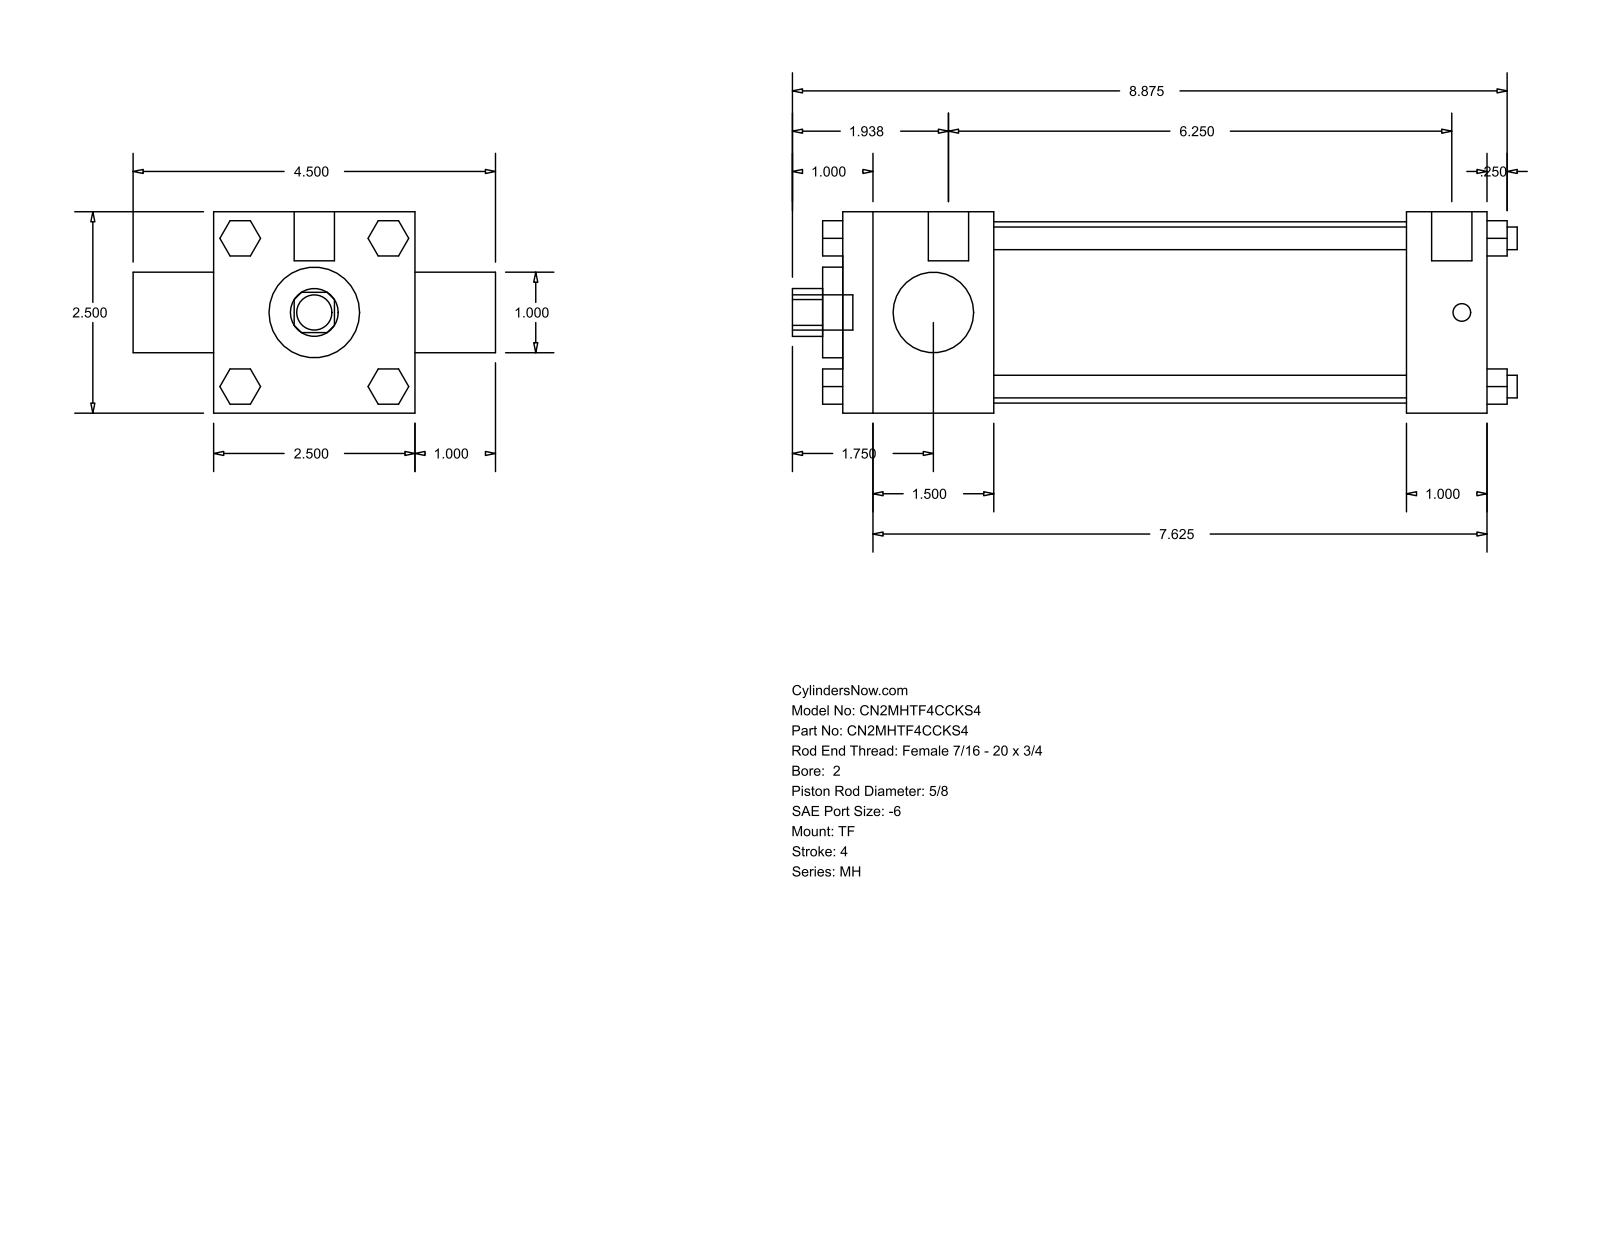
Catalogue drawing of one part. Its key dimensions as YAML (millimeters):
part_name: "MH_TF__0200_0.625"
step_written_by: "GSSL Pune (CONFIG_CONTROL_DESIGN)"
units: millimeters
bodies: {solids: 0, faces: 120, planar: 92, cylindrical: 28, other: 0}
overall_size: [228.6, 114.3, 63.5]
round_holes:
  - {diameter: 15.88, count: 1}
  - {diameter: 25.4, count: 1}
  - {diameter: 28.57, count: 1}
  - {diameter: 57.15, count: 1}
round_bosses_or_shafts:
  - {diameter: 7.14, count: 4}
  - {diameter: 5.56, count: 3}
  - {diameter: 12.7, count: 2}
  - {diameter: 11.11, count: 1}
partial_cylinders:
  - {radius: 7.54, count: 1}
face_to_face_distances: [63.5, 203.19, 47.62, 177.8, 130.18, 155.57, 25.39, 25.4, 88.9, 6.35]
